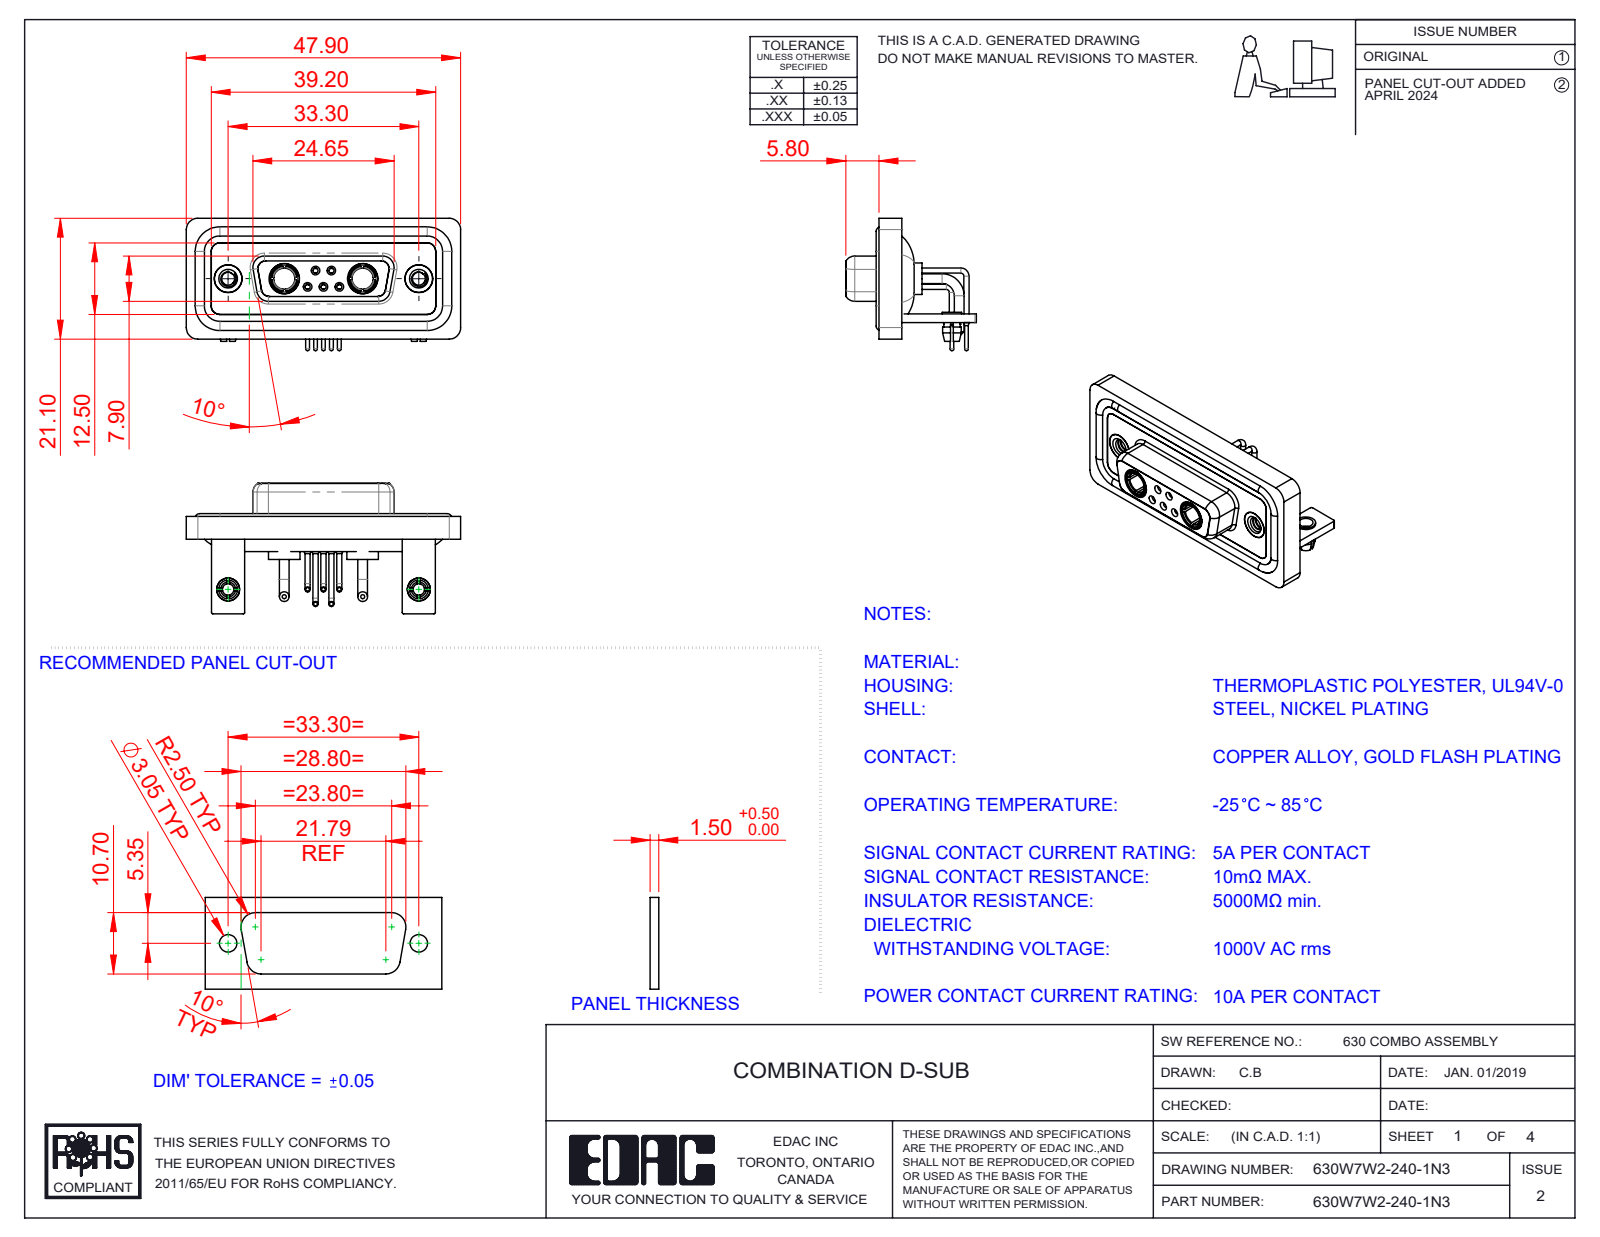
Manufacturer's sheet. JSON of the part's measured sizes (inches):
{"part_name": "630Combo Threaded Rivet_2; 630Combo Stabilizer Bracket_50 Contacts; 630Combo Housing_7W2; Power Socket_10A RA (+7 more)", "step_written_by": "SolidWorks 2023 (CONFIG_CONTROL_DESIGN)", "units": "inches", "bodies": {"solids": 20, "faces": 947, "planar": 306, "cylindrical": 409, "other": 232}, "overall_size": [1.886, 0.91, 0.898], "volume_in3": 0.396, "surface_area_in2": 17.13, "round_holes": [[0.079, 7], [0.035, 5], [0.043, 5], [0.059, 5], [0.191, 4], [0.063, 3], [0.067, 2], [0.089, 2], [0.098, 2], [0.126, 2], [0.146, 2], [0.157, 2]], "round_bosses_or_shafts": [[0.063, 6], [0.035, 5], [0.026, 5], [0.067, 4], [0.217, 2], [0.205, 2], [0.195, 2], [0.195, 2]], "partial_cylinders_radius": [[0.079, 21], [0.059, 18], [0.01, 16], [0.053, 12], [0.063, 8], [0.02, 5], [0.024, 4], [0.026, 4]], "face_to_face_distances": [0.016, 0.114, 0.059, 0.071, 0.146, 0.043, 0.161, 0.063, 0.098, 0.055], "hole_center_spacings": [0.124, 0.109, 0.386, 0.925, 1.311, 0.17, 0.17, 0.198]}
